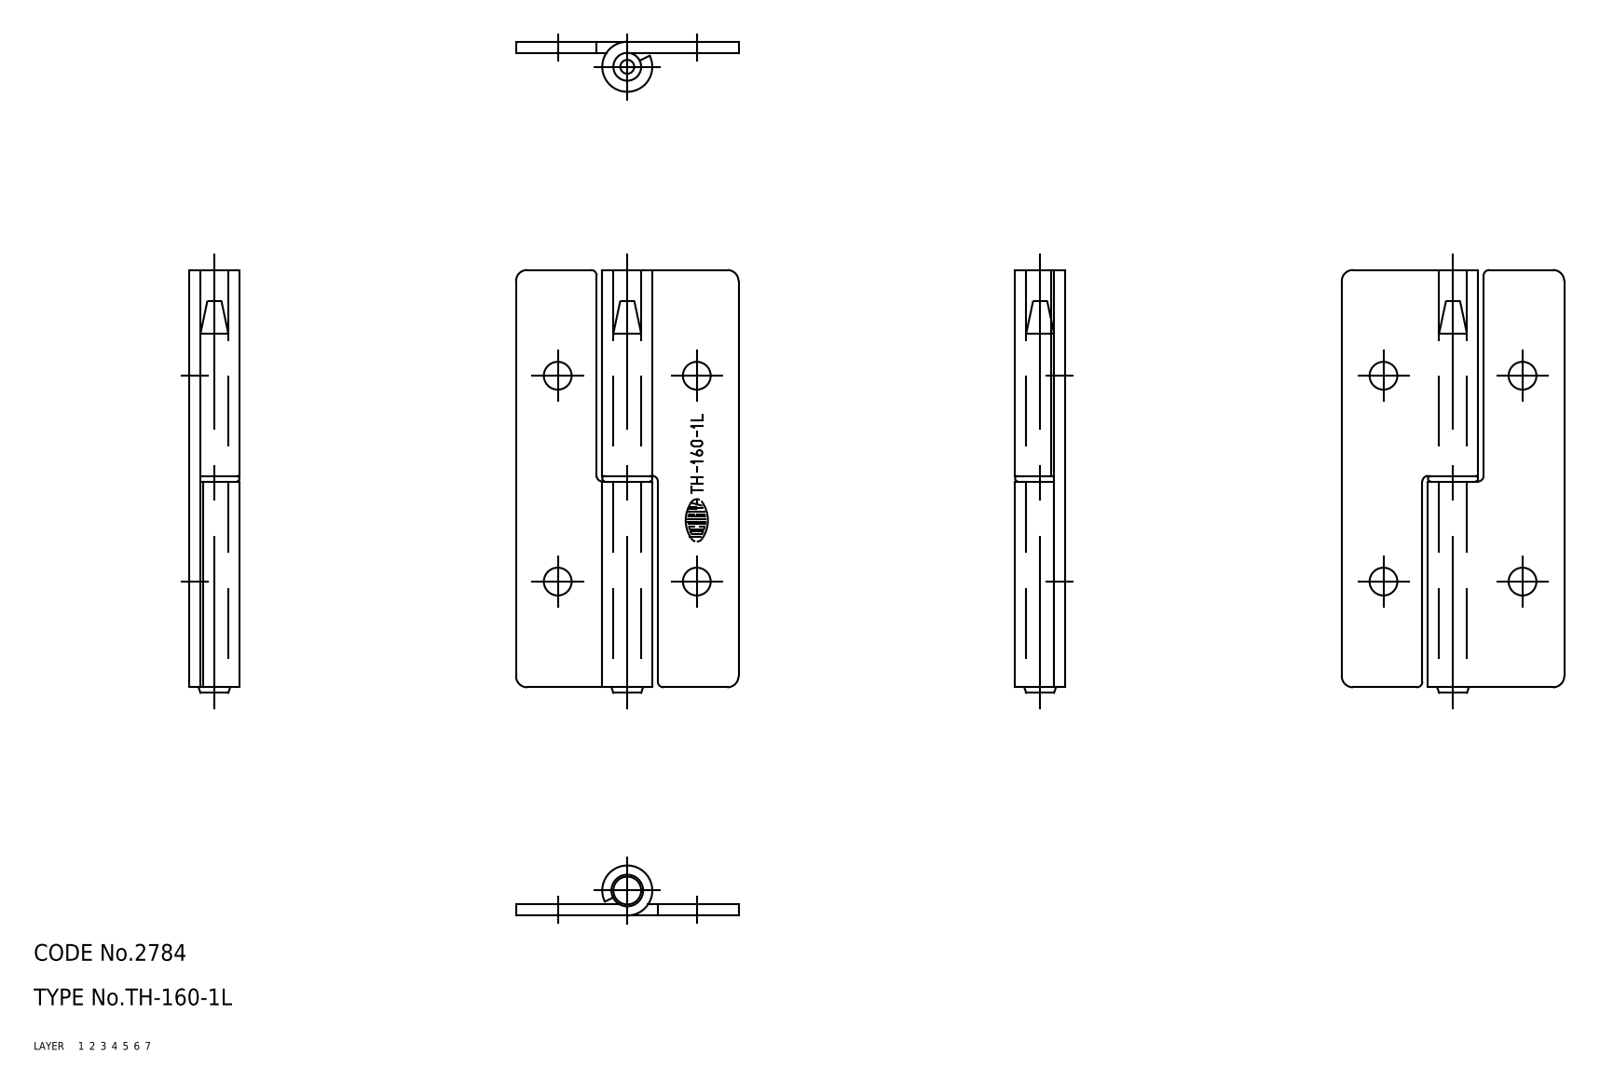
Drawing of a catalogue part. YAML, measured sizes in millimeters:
part_name: "67112052; 67112065; 67112078"
step_written_by: "CADfix (AUTOMOTIVE_DESIGN)"
units: millimeters
bodies: {solids: 3, faces: 53, planar: 0, cylindrical: 0, other: 53}
overall_size: [76, 40, 9]
volume: 9063
surface_area: 9908
